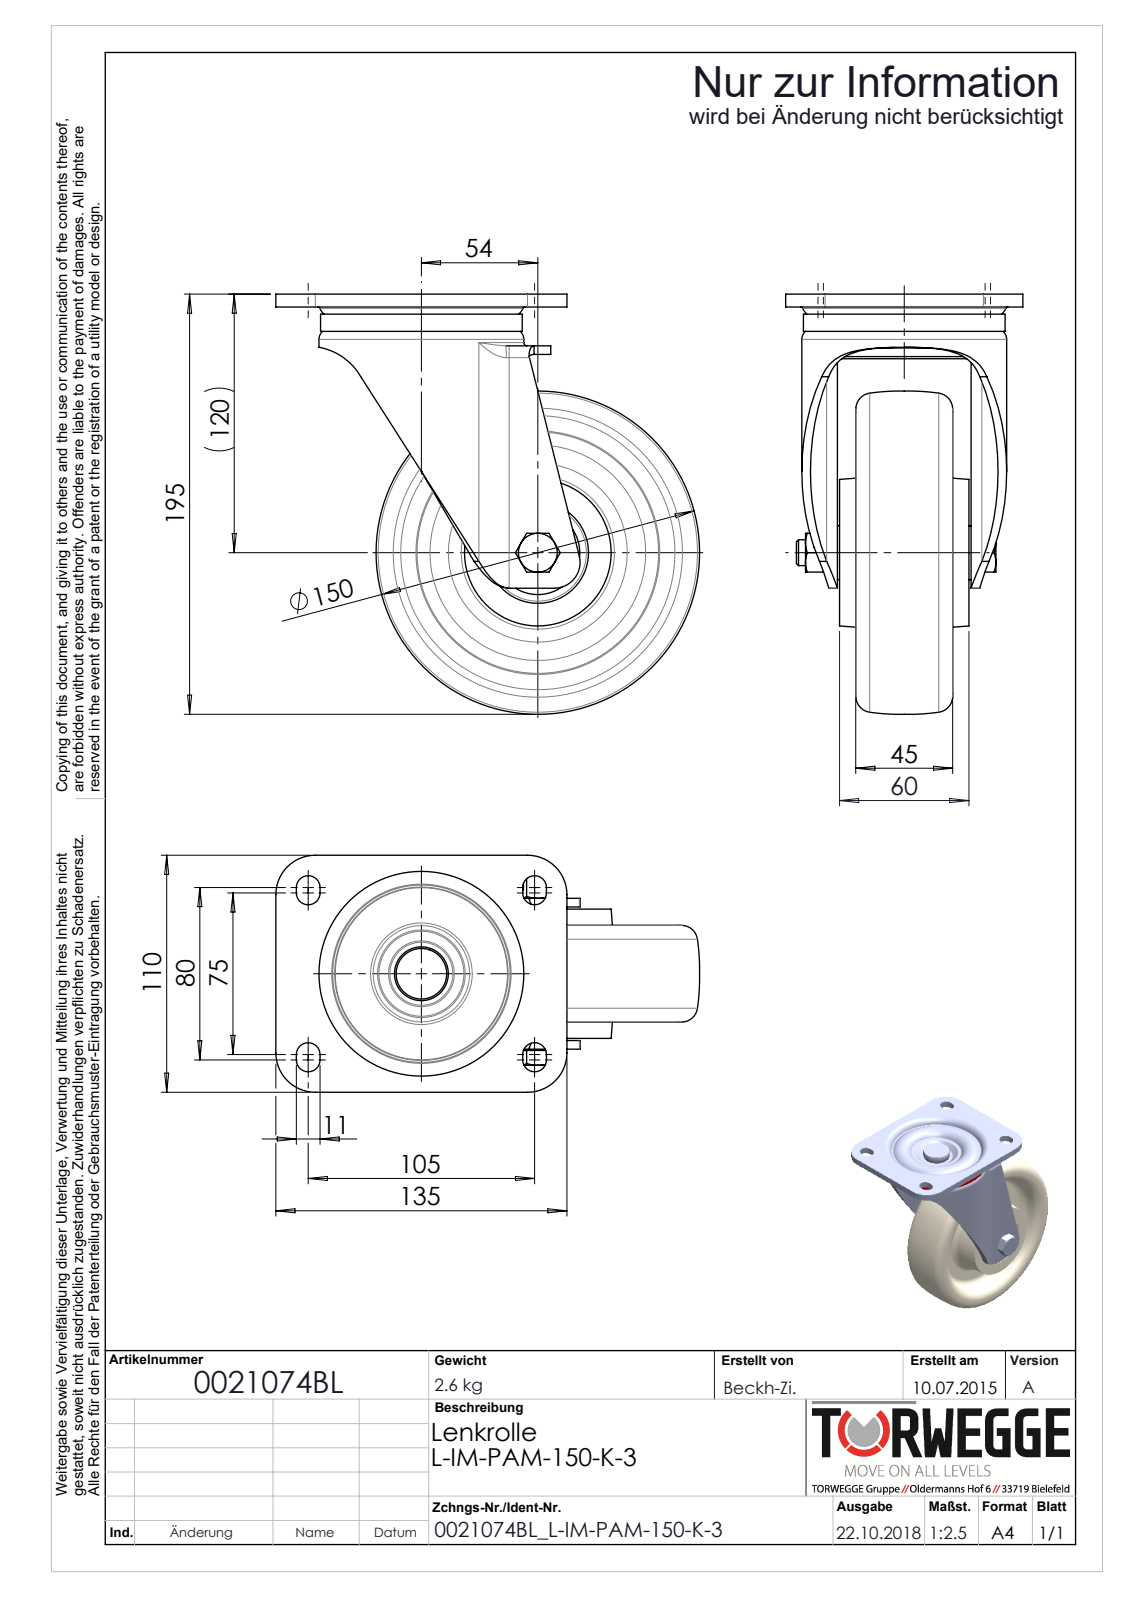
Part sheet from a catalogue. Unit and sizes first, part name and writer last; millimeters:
Units: millimetres
Overall size (bounding box): 196.52 × 195.02 × 110
Round holes (diameter × count): ⌀10.2 ×1, ⌀12 ×1, ⌀12.2 ×1, ⌀16.2 ×1, ⌀20 ×1, ⌀35 ×1, ⌀38.9 ×1, ⌀40 ×1, ⌀40.2 ×1, ⌀55.6 ×1, ⌀80.46 ×1, ⌀87 ×1
Round bosses / shafts (diameter × count): ⌀18 ×2, ⌀95 ×1, ⌀93.54 ×1, ⌀61.97 ×1, ⌀47 ×1, ⌀28.1 ×1, ⌀25 ×1, ⌀19.9 ×1
Partial cylindrical surfaces — rounded edges, fillets, slot ends (radius × count): R5.5 ×10, R0.31 ×8, R0.17 ×7, R0.51 ×7, R0.1 ×4, R0.72 ×4, R0.78 ×4, R18.29 ×4
Main face-to-face distances: 6, 4, 1, 25, 10, 26, 30, 5, 12.5, 35
Volume: 825 561 mm³ · Surface area: 216 244 mm²
Bodies: 14 solids, 714 faces (322 planar, 180 cylindrical, 212 other)
Part name (STEP PRODUCT): 0021074K_L-IM-PAM-150-K-3
STEP written by: SolidWorks 2014 (AUTOMOTIVE_DESIGN)
